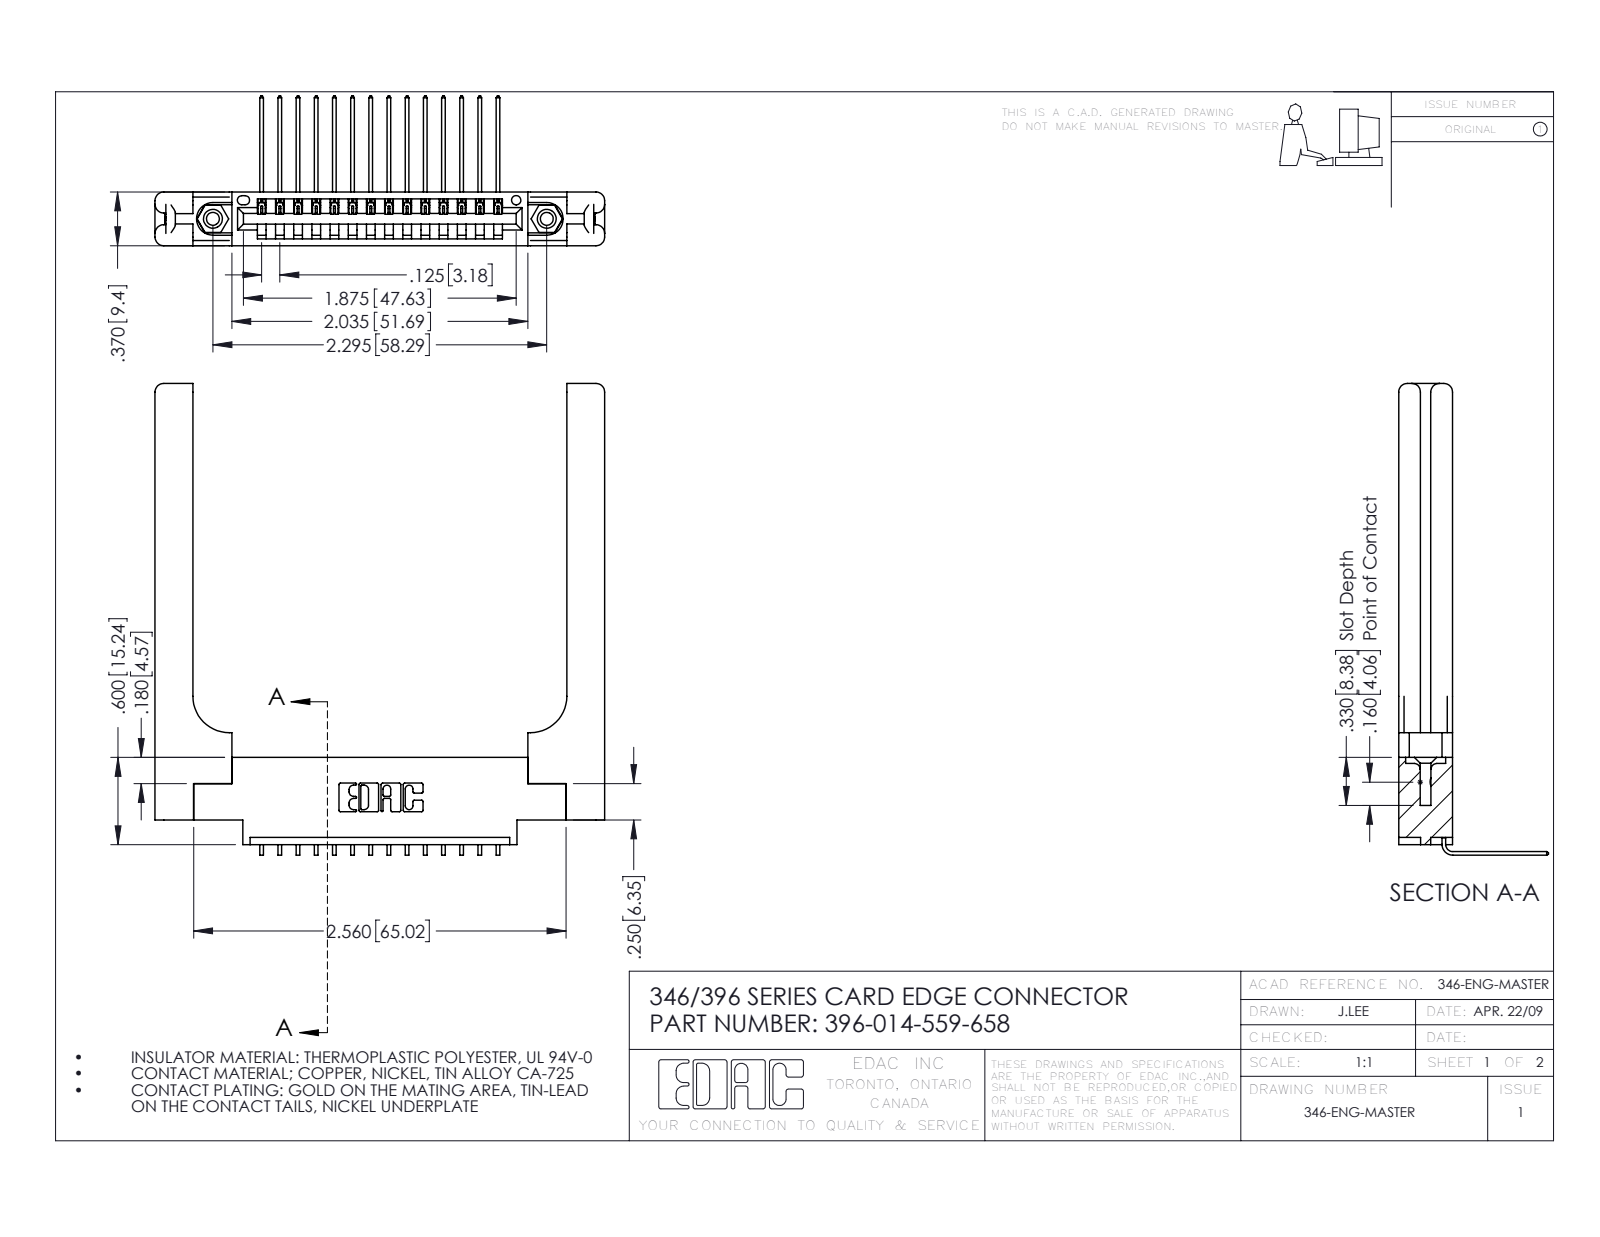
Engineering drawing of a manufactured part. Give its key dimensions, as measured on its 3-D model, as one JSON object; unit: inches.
{"part_name": "346-220-058_345-220-058; 345-292-001_558 559 Tail - 1; 396-014-559-658; 346 Part_0.170 Offset - 0.156 Dia-TH (+1 more)", "step_written_by": "SolidWorks 2016 (CONFIG_CONTROL_DESIGN)", "units": "inches", "bodies": {"solids": 19, "faces": 1222, "planar": 816, "cylindrical": 346, "other": 60}, "overall_size": [3.243, 3.091, 1.03], "volume_in3": 0.899, "surface_area_in2": 22.2, "round_holes": [[0.089, 2], [0.125, 2], [0.156, 2], [0.064, 1]], "round_bosses_or_shafts": [[0.155, 2]], "partial_cylinders_radius": [[0.006, 28], [0.01, 22], [0.06, 16], [0.007, 6], [0.031, 6], [0.026, 3], [0.03, 2], [0.031, 2]], "face_to_face_distances": [0.37, 0.15, 0.072, 0.148, 0.048, 0.322, 0.22, 0.102, 0.173, 0.25], "hole_center_spacings": [0.246, 2.089, 2.295]}
